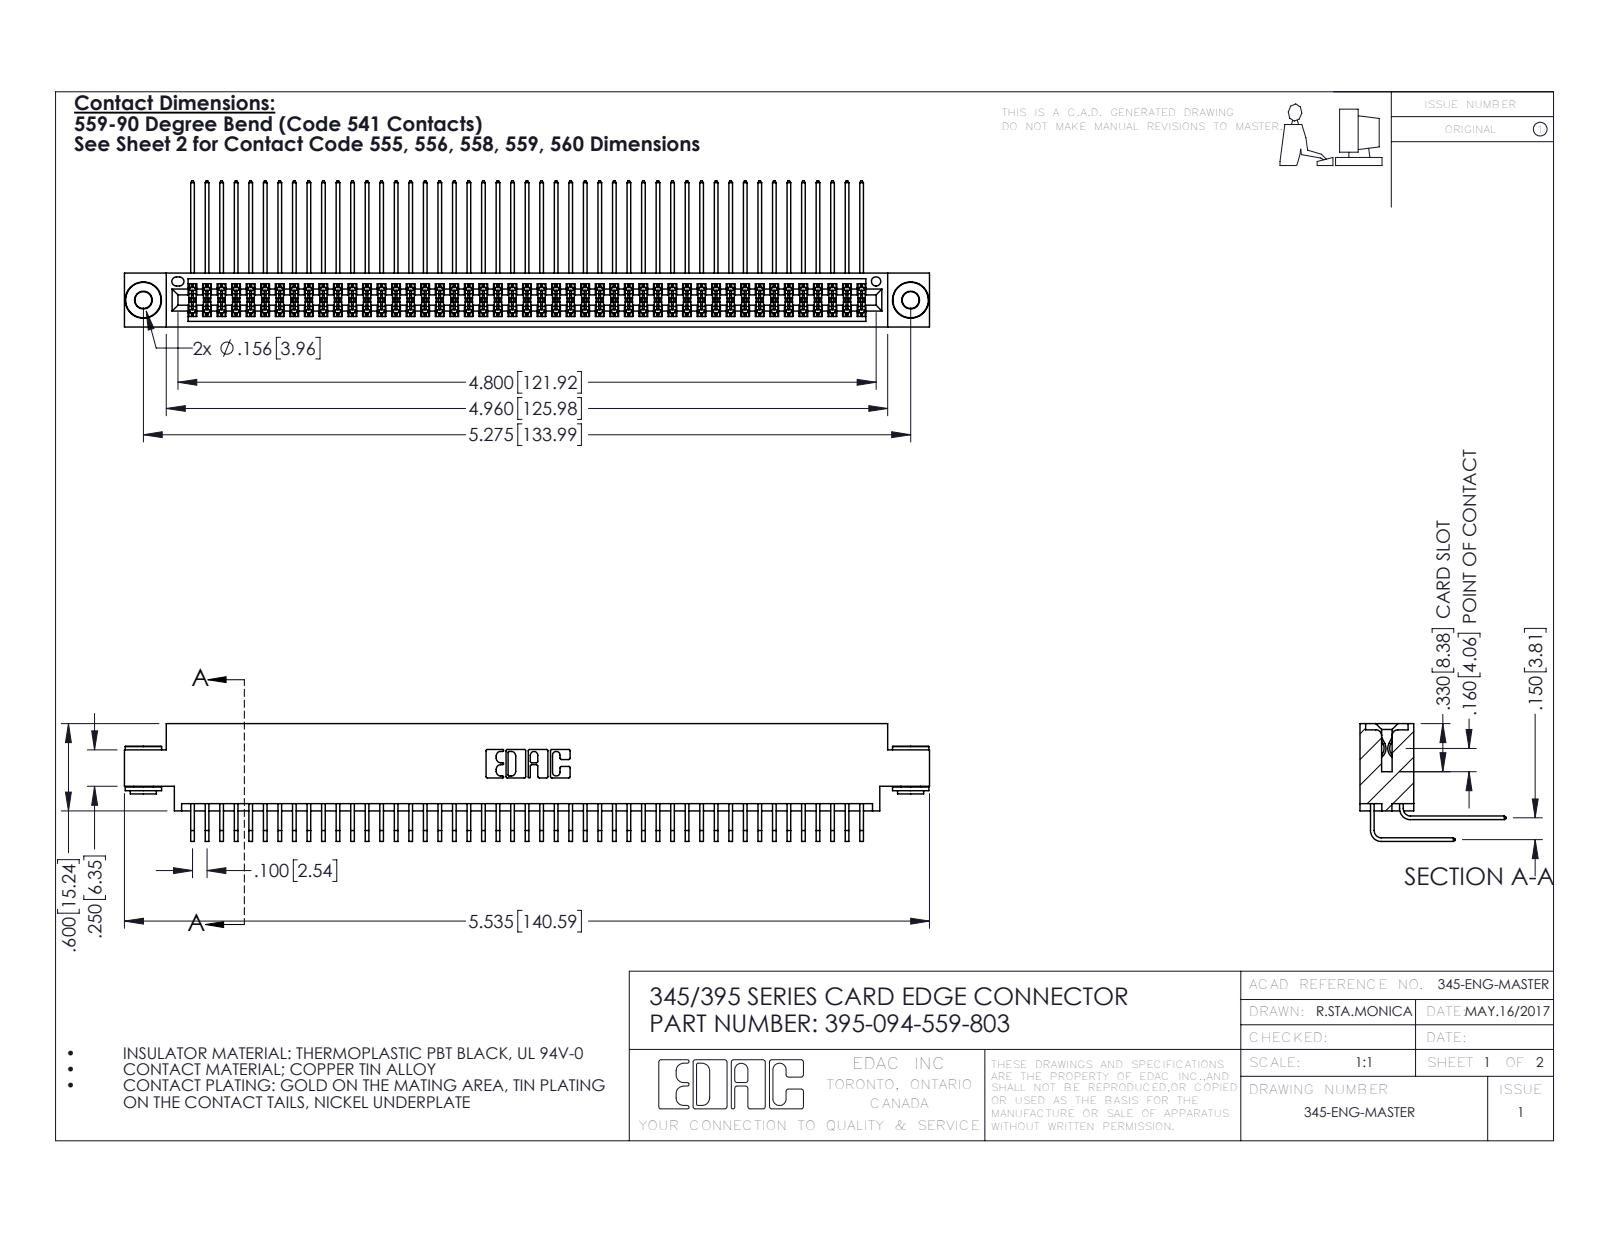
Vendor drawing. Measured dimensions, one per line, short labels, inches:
name: 345 Part_0.170 Offset - 0.156 Dia-TH; 345-292-001_559 Tail - 2; 345-292-001_558 559 Tail - 1; 345-250-002_345-250-002-102 (+1 more)
written by: SolidWorks 2016 (CONFIG_CONTROL_DESIGN)
unit: in
bodies: 97 solids, 5056 faces (3384 planar, 1664 cylindrical, 8 other)
size: 5.535 × 1.005 × 0.809
volume: 0.864 in³; area: 37.07 in²
holes: 2× ⌀0.116, 2× ⌀0.156, 1× ⌀0.064
bosses: 2× ⌀0.25, 2× ⌀0.18, 2× ⌀0.136
rounds: 141× R0.006, 22× R0.01, 6× R0.007, 6× R0.031, 3× R0.026, 2× R0.014, 2× R0.019, 2× R0.022
face distances: 0.072, 0.298, 0.37, 0.2, 0.098, 0.272, 0.025, 0.175, 0.225, 0.15
hole spacings: 0.27, 5.039, 5.275
